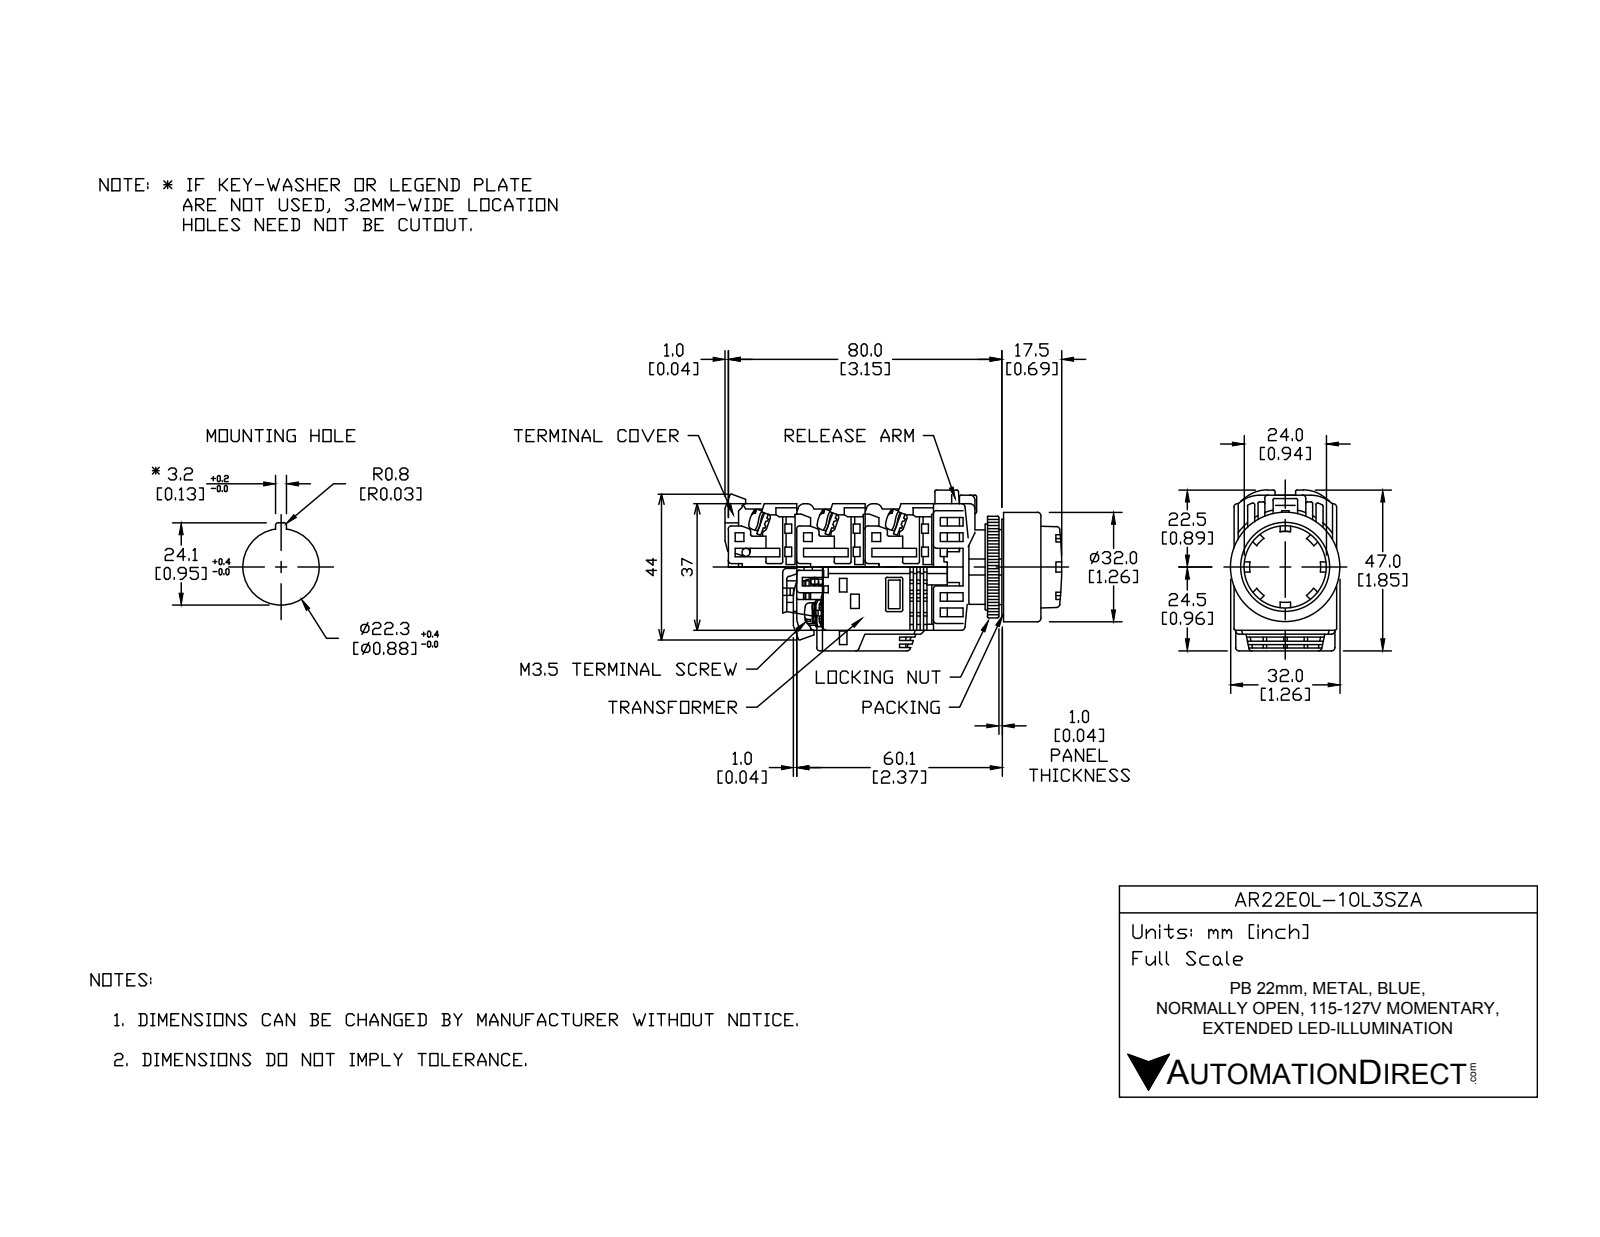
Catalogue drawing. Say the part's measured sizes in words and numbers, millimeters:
The part is named "AR22E0L-10L3SZA". Its 3-D file was written by "SolidWorks 2017 (AUTOMOTIVE_DESIGN)". It is 16 solids with 451 faces: 317 planar, 99 cylindrical and 35 other. Overall it measures 79.25 by 43.81 by 32 millimeters. Its volume is 50 413 cubic millimeters and its surface area 26 207 square millimeters. Round holes: 1 of diameter 21.8, 1 of diameter 22, 1 of diameter 25, 1 of diameter 31. Round bosses or shafts: 4 of diameter 5, 1 of diameter 32, 1 of diameter 30.5, 1 of diameter 29.8, 1 of diameter 24, 1 of diameter 23.8, 1 of diameter 21.75, 1 of diameter 17. Partial cylindrical surfaces (rounded edges, fillets, slot ends): 32 of radius 0.5, 8 of radius 1.75, 4 of radius 5, 2 of radius 4, 1 of radius 16.59, 1 of radius 17.59. The main face-to-face distances are 1, 18, 29, 20, 28.5, 3, 2, 21, 0.35, 7.5.
